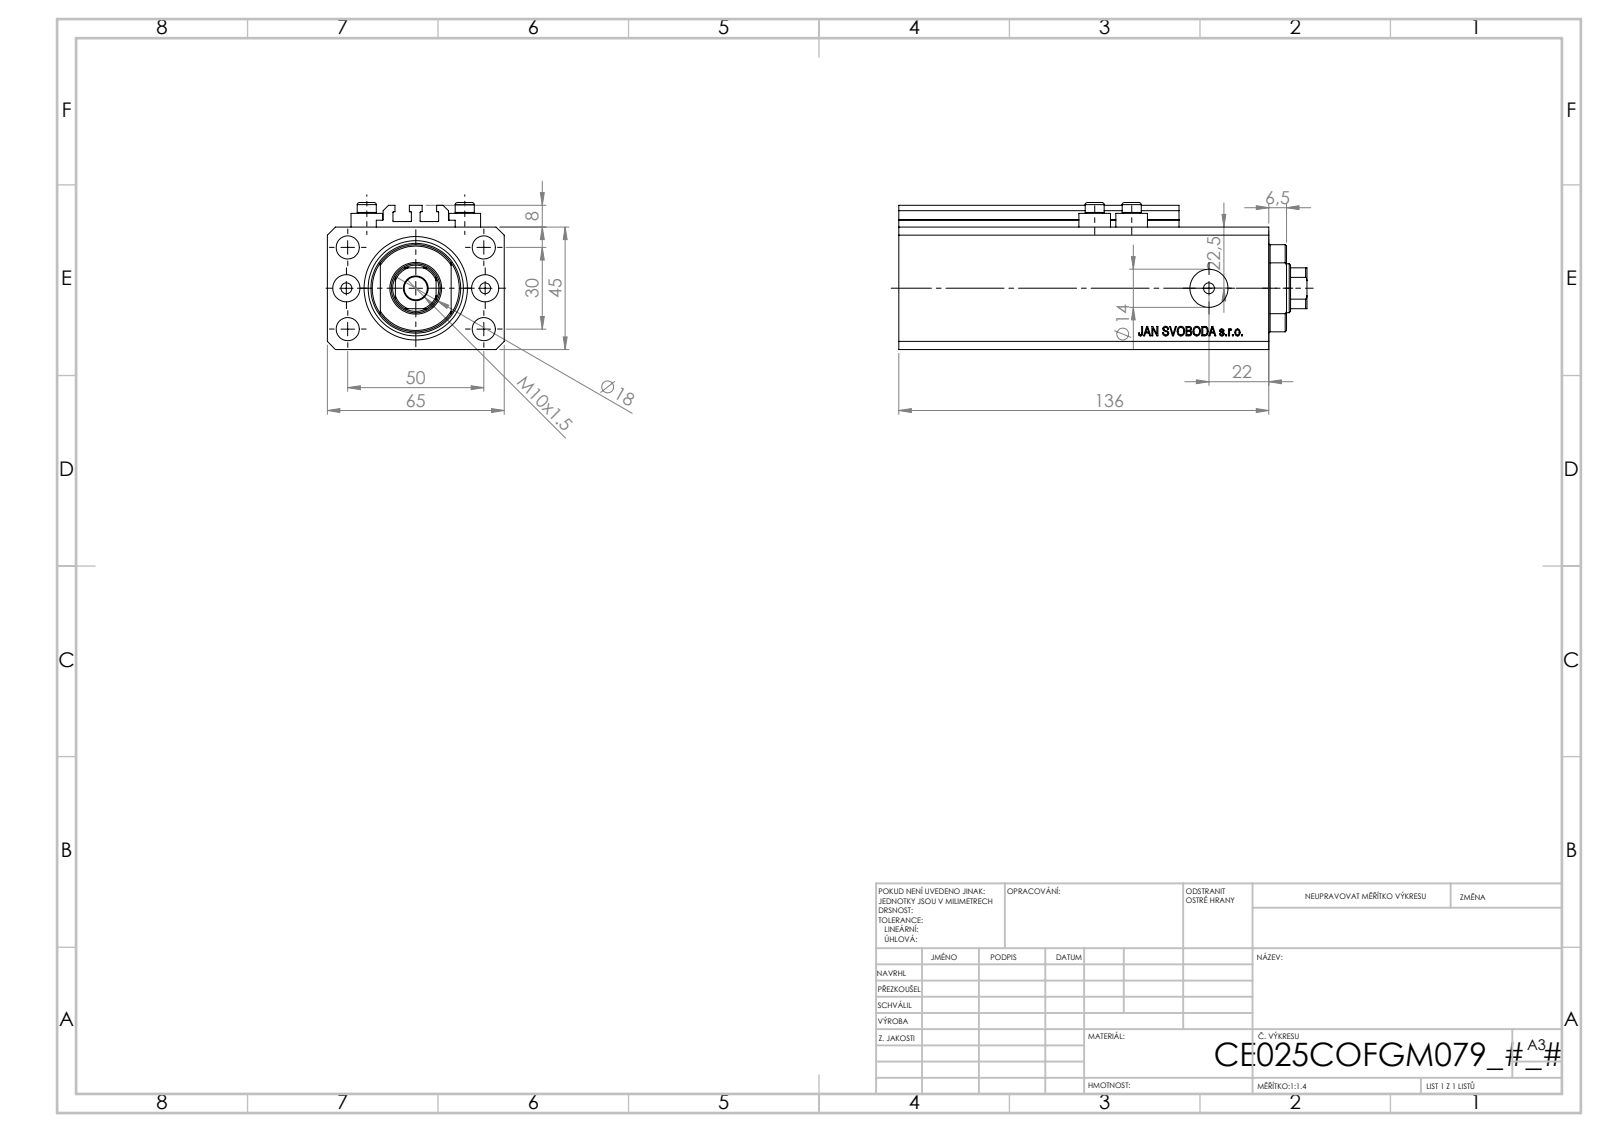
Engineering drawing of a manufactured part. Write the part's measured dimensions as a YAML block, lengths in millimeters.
part_name: "V250CE_C_Body; V250CE_C_VCP; ALLEN BOLT V250CE; V250CE_VC_C"
step_written_by: "SolidWorks 2019 (CONFIG_CONTROL_DESIGN)"
units: millimeters
bodies: {solids: 8, faces: 1034, planar: 504, cylindrical: 86, other: 444}
overall_size: [150, 65, 54]
volume: 363557
surface_area: 90050
round_holes:
  - {diameter: 4, count: 8}
  - {diameter: 8.5, count: 5}
  - {diameter: 10, count: 2}
  - {diameter: 14, count: 2}
  - {diameter: 18, count: 1}
  - {diameter: 25, count: 1}
  - {diameter: 38, count: 1}
round_bosses_or_shafts:
  - {diameter: 11.6, count: 4}
  - {diameter: 7, count: 4}
partial_cylinders:
  - {radius: 0.2, count: 10}
  - {radius: 8.5, count: 1}
  - {radius: 16, count: 1}
face_to_face_distances: [45, 65, 47, 14, 122, 136, 2.5, 2, 10, 20.5]
hole_center_spacings: [15.01, 29.15, 52.68, 13.6, 25.5, 30, 36, 38.48]
